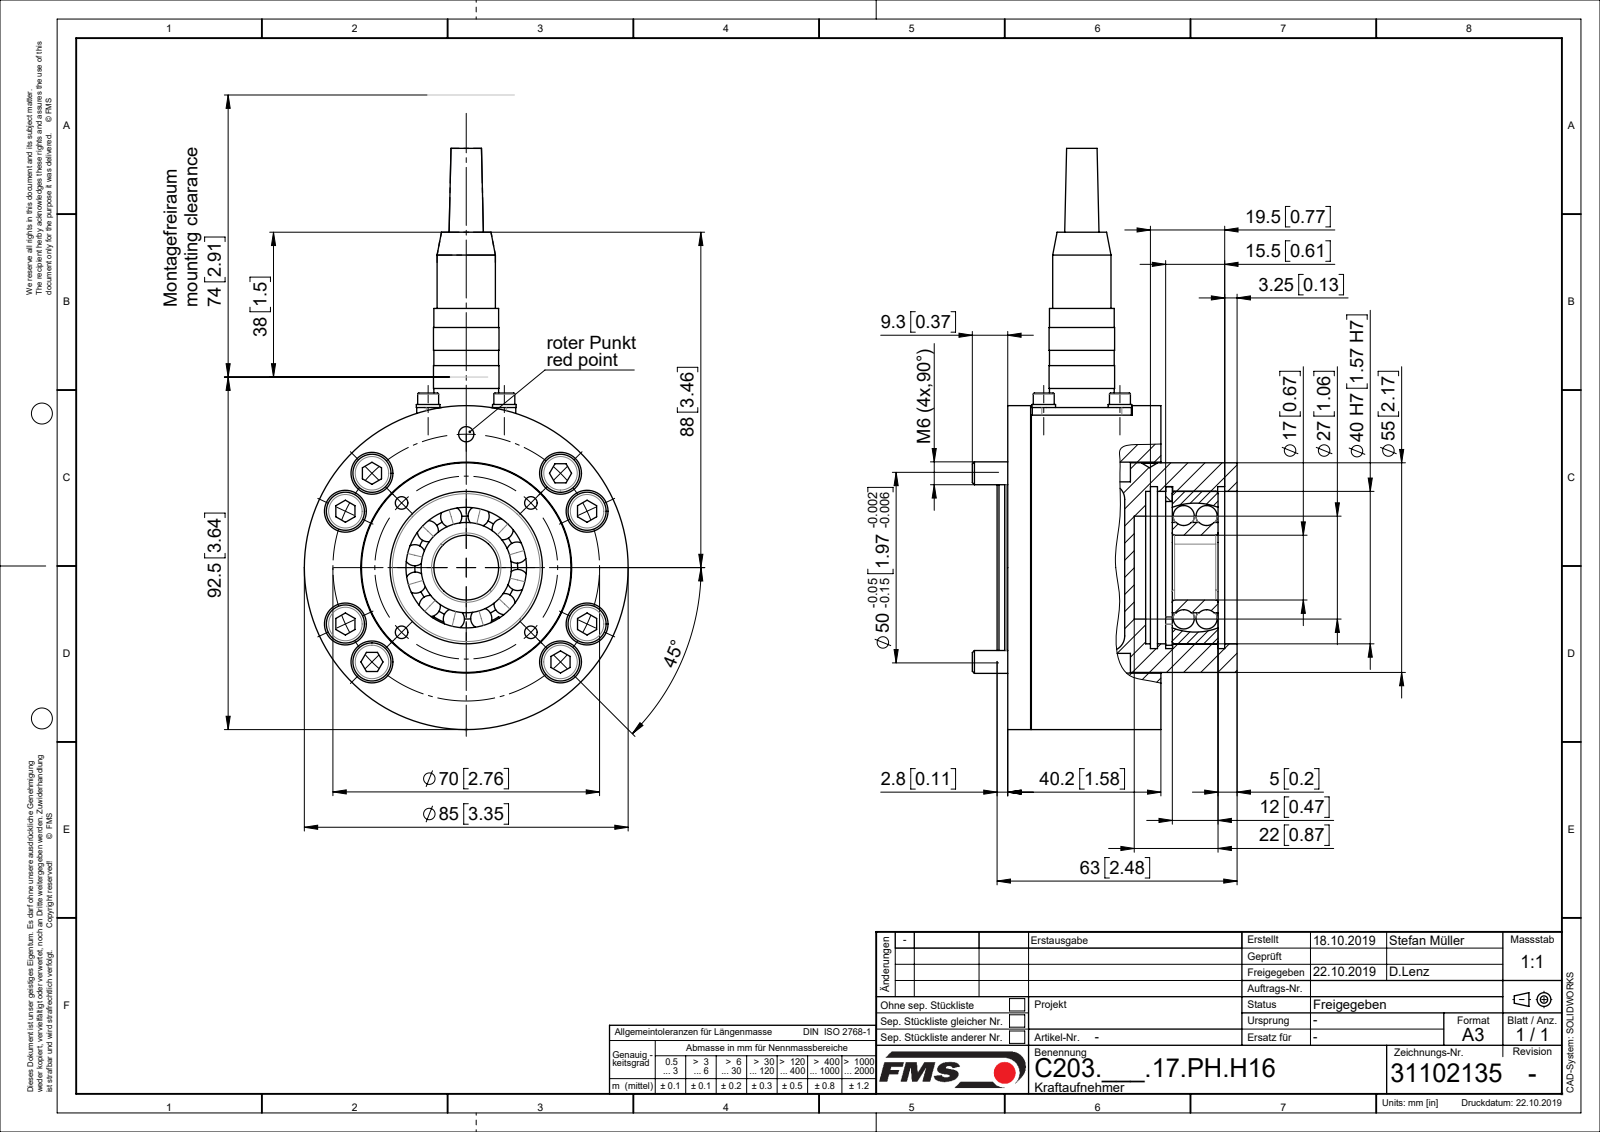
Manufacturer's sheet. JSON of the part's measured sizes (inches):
{"part_name": "C0710091; C0709071; C0704203; C0709072 (+8 more)", "step_written_by": "Mechanical Desktop 2007 (CONFIG_CONTROL_DESIGN)", "units": "inches", "bodies": {"solids": 27, "faces": 530, "planar": 183, "cylindrical": 249, "other": 98}, "overall_size": [6.004, 3.346, 2.848], "volume_in3": 15.23, "surface_area_in2": 130.5, "round_holes": [[0.256, 8], [0.433, 8], [0.102, 4], [0.126, 4], [0.135, 4], [0.203, 4], [0.276, 4], [0.157, 1], [0.42, 1], [0.472, 1], [0.591, 1], [0.669, 1]], "round_bosses_or_shafts": [[0.394, 8], [0.236, 8], [0.059, 5], [0.244, 4], [0.217, 4], [0.197, 4], [0.118, 4], [3.346, 1]], "partial_cylinders_radius": [[0.098, 4], [0.197, 2]], "face_to_face_distances": [0.236, 0.118, 1.575, 1.339, 1.693, 0.157, 0.965, 0.354, 0.591, 1.929], "hole_center_spacings": [1.378, 1.671, 0.787, 0.433, 0.479, 0.557, 0.587, 0.945]}
